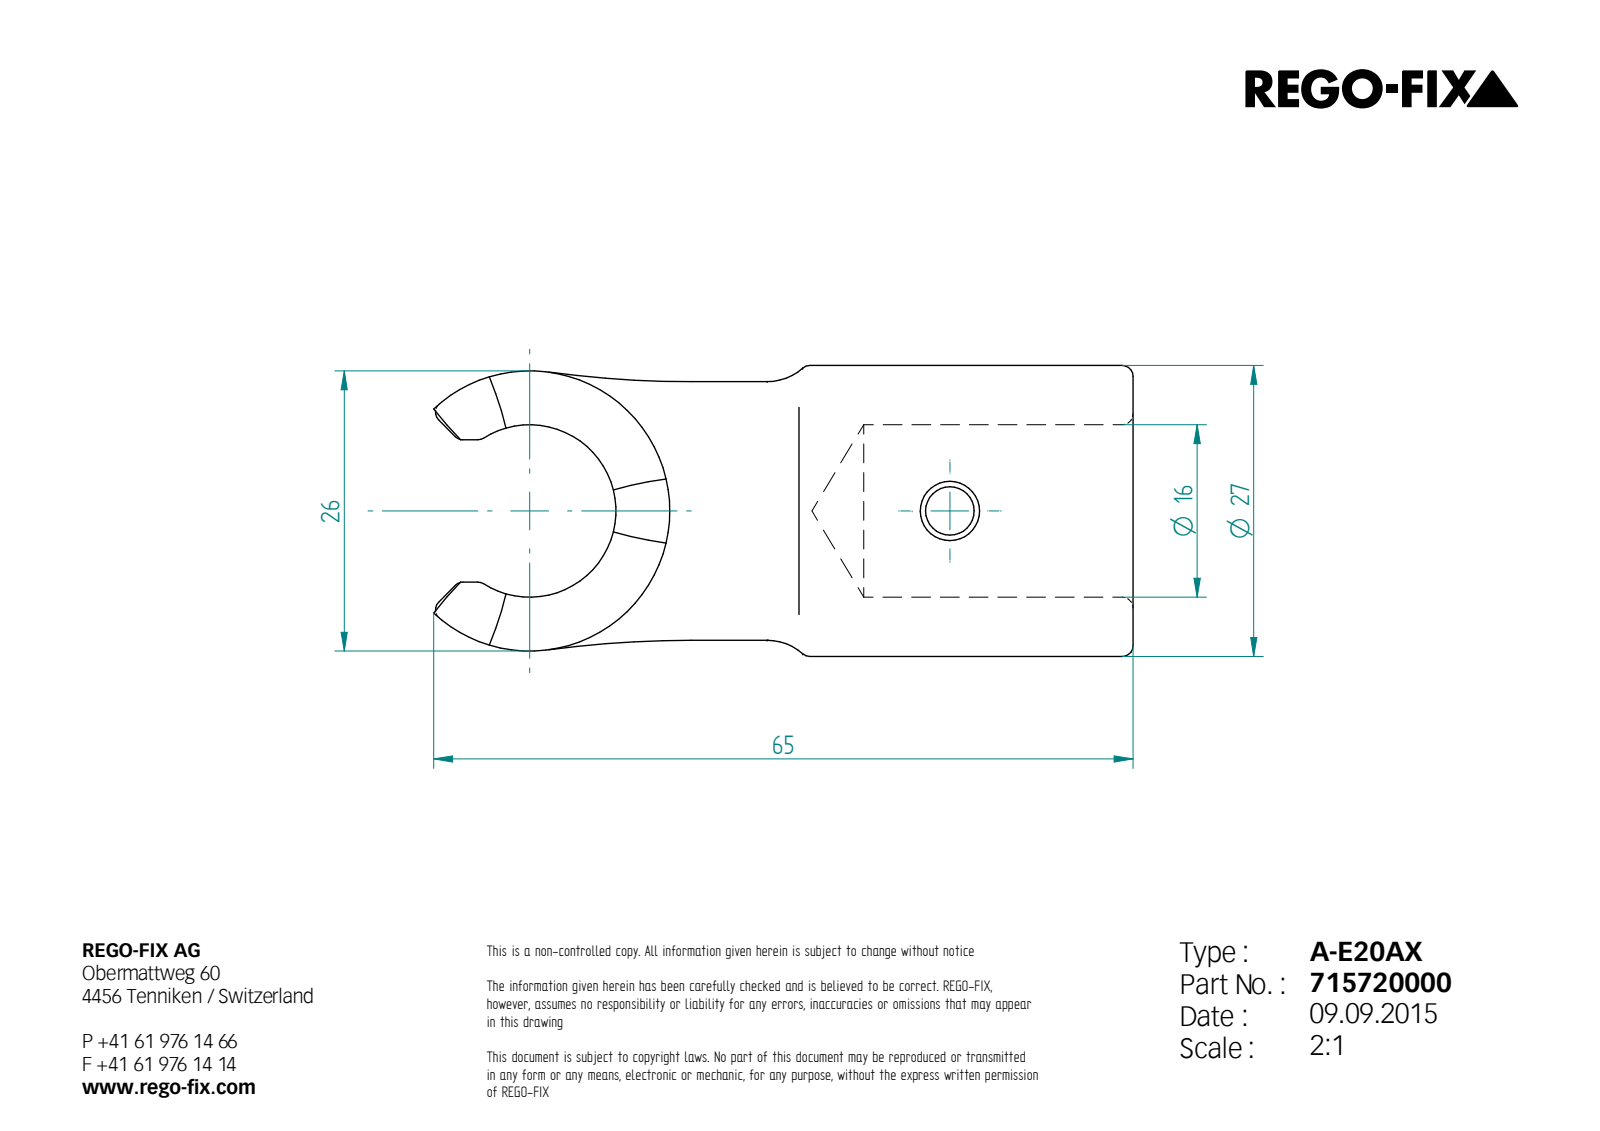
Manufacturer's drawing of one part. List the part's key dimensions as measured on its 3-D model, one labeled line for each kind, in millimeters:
STEP written by: Unknown (AUTOMOTIVE_DESIGN)
Units: millimetres
Bodies: 1 solid, 86 faces (22 planar, 29 cylindrical, 35 other)
Overall size (bounding box): 64.9 × 27 × 27
Volume: 17 408 mm³ · Surface area: 7 320 mm²
Round holes (diameter × count): ⌀4.5 ×1, ⌀5.5 ×1, ⌀16 ×1
Round bosses / shafts (diameter × count): ⌀27 ×1
Partial cylindrical surfaces — rounded edges, fillets, slot ends (radius × count): R1 ×6, R2 ×6, R32.52 ×3, R5 ×2, R100 ×2, R8 ×1, R13 ×1
Main face-to-face distances: 6, 12, 31, 14, 8, 2, 5.4, 18.6, 13.2, 24
